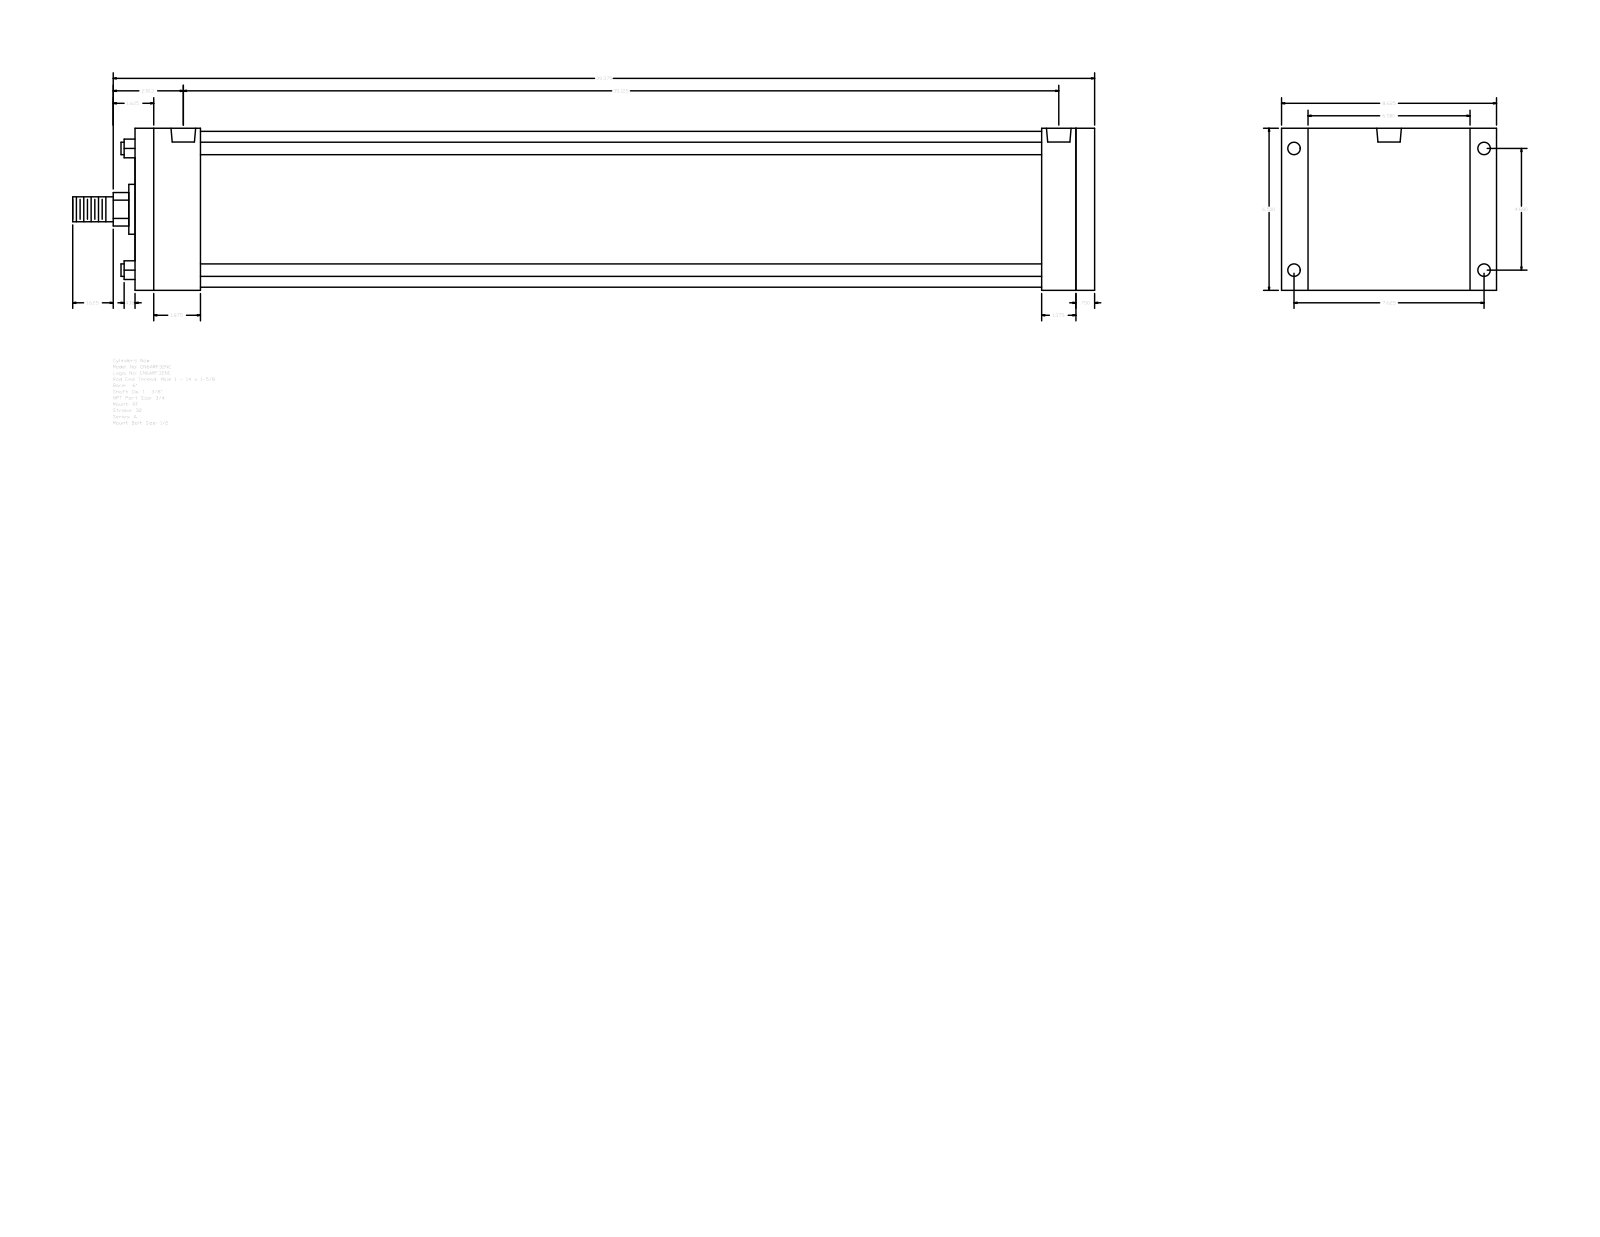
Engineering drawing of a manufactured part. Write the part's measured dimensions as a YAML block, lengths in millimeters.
part_name: "A_RF__0600_1.375"
step_written_by: "GSSL Pune (CONFIG_CONTROL_DESIGN)"
units: millimeters
bodies: {solids: 0, faces: 92, planar: 64, cylindrical: 28, other: 0}
overall_size: [1041.4, 219.07, 165.1]
round_holes:
  - {diameter: 12.7, count: 4}
  - {diameter: 15.08, count: 4}
  - {diameter: 25.12, count: 2}
round_bosses_or_shafts:
  - {diameter: 12.7, count: 4}
  - {diameter: 158.75, count: 1}
  - {diameter: 50.8, count: 1}
  - {diameter: 34.92, count: 1}
  - {diameter: 25.4, count: 1}
partial_cylinders:
  - {radius: 17.06, count: 1}
face_to_face_distances: [165.1, 977.89, 958.85, 19.04, 53.97, 66.67, 892.18, 911.22, 923.92, 857.25]
hole_center_spacings: [5.56, 123.96, 193.68, 229.95, 881.05, 886.61, 892.17]
